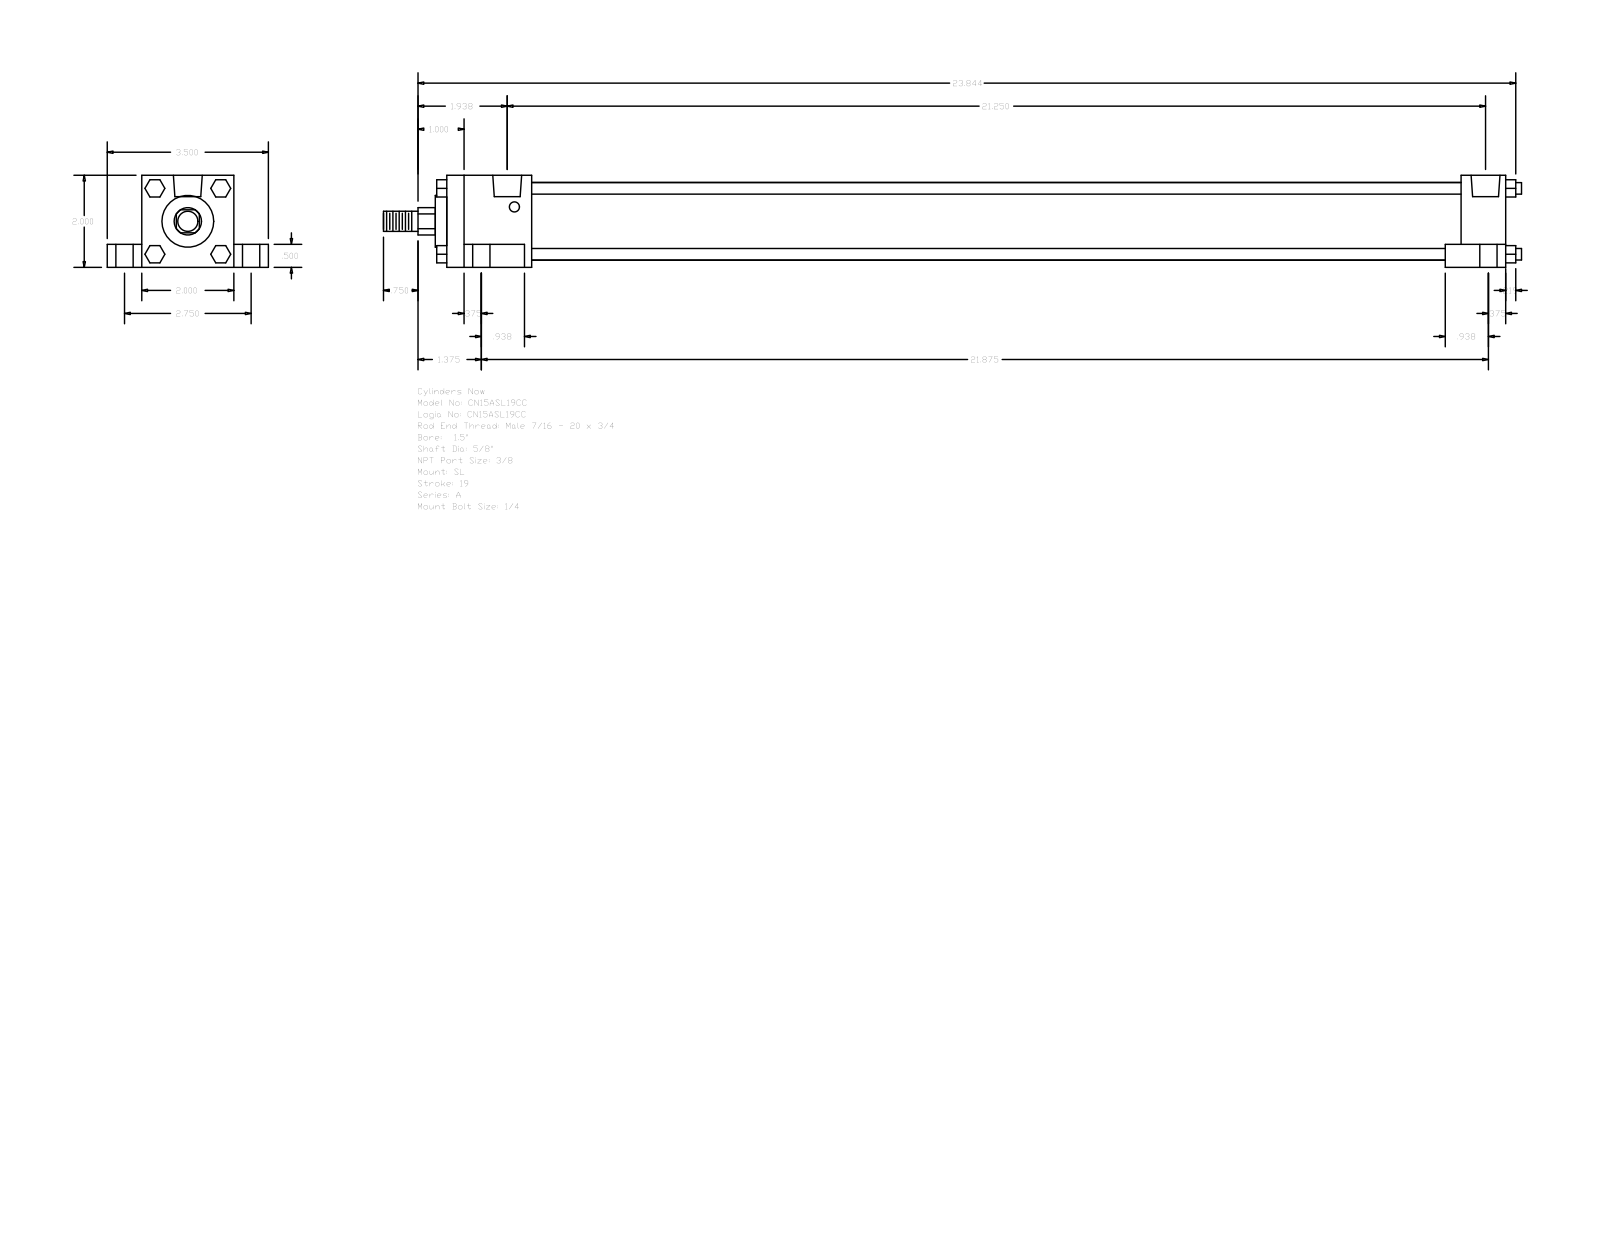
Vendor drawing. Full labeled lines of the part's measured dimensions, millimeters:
Part name (STEP PRODUCT): A_SL__0150_0.625
STEP written by: GSSL Pune (CONFIG_CONTROL_DESIGN)
Units: millimetres
Bodies: 0 solids, 148 faces (112 planar, 36 cylindrical, 0 other)
Overall size (bounding box): 627.86 × 88.9 × 50.8
Round holes (diameter × count): ⌀5.56 ×4, ⌀9.53 ×4, ⌀15.88 ×4, ⌀15.93 ×2
Round bosses / shafts (diameter × count): ⌀6.35 ×4, ⌀42.93 ×1, ⌀28.57 ×1, ⌀15.88 ×1, ⌀11.11 ×1
Partial cylindrical surfaces — rounded edges, fillets, slot ends (radius × count): R7.54 ×1
Main face-to-face distances: 50.8, 19.05, 38.1, 12.7, 69.85, 584.2, 9.52, 33.34, 559.59, 24.61
Hole centre spacings: 3.97, 34.96, 35.36, 37.73, 39.41, 69.84, 531.81, 535.78
